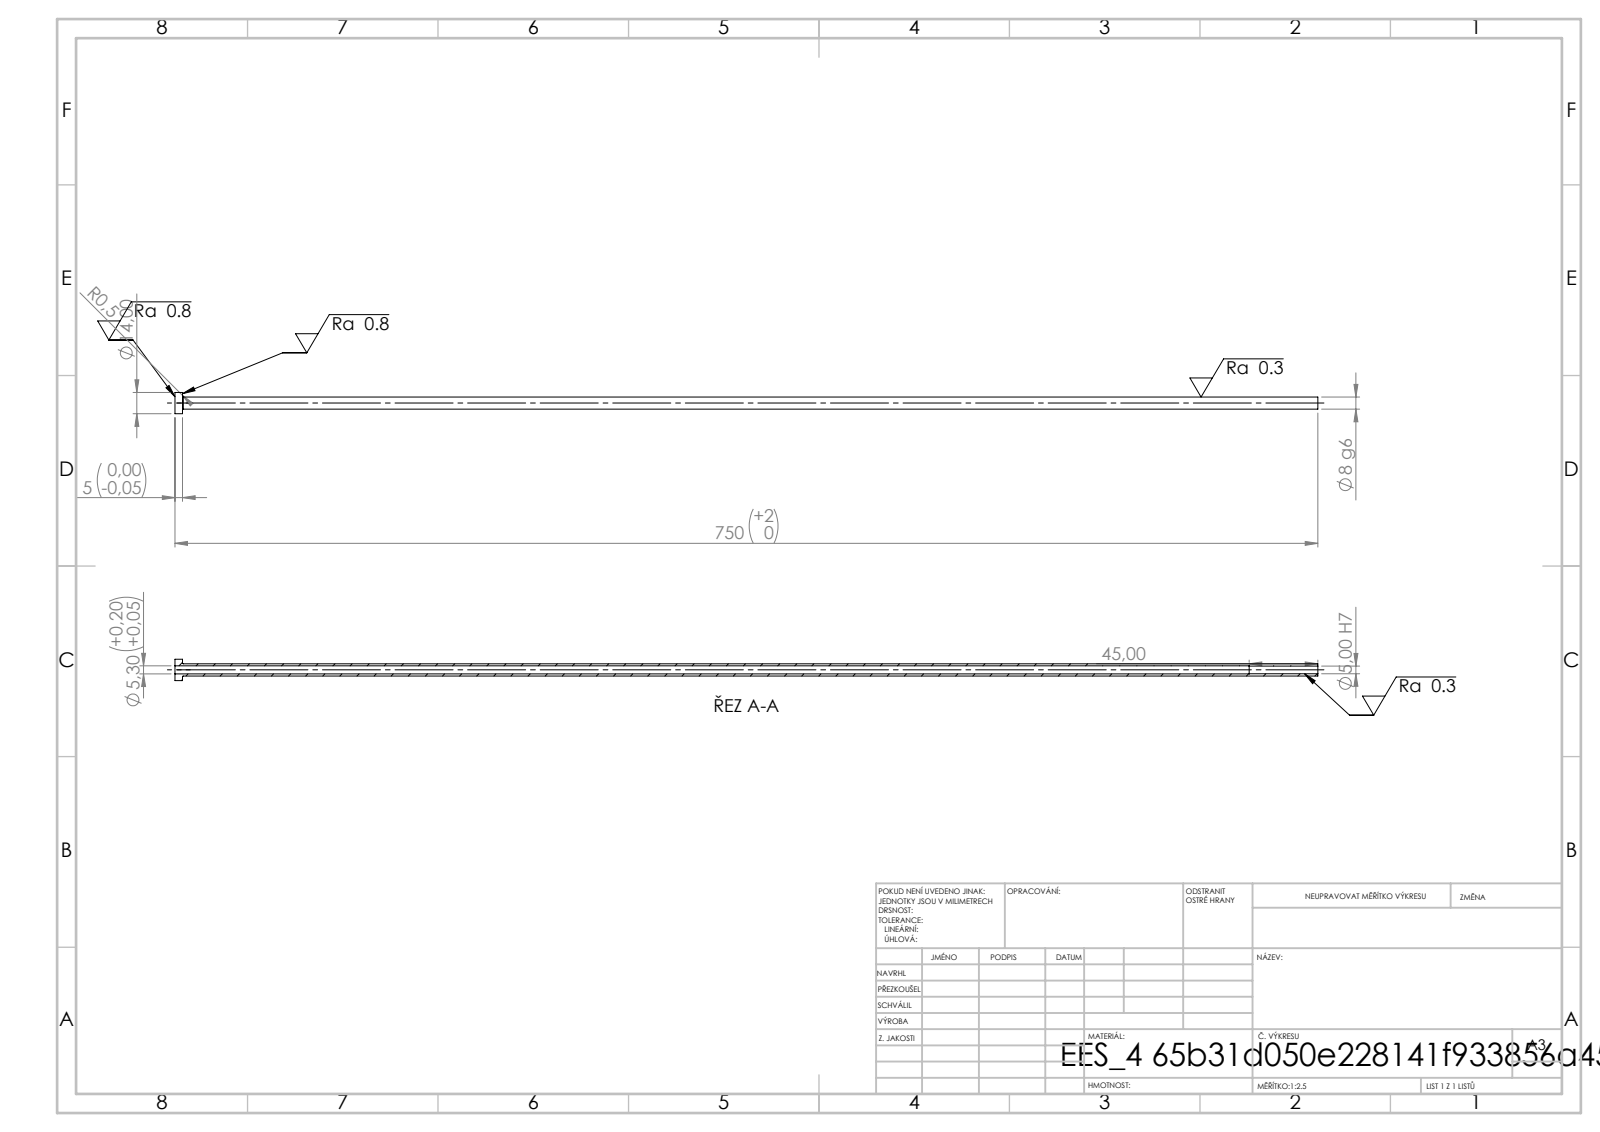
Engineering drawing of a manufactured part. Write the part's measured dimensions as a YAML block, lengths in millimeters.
step_written_by: "SolidWorks 2019 (CONFIG_CONTROL_DESIGN)"
units: millimeters
bodies: {solids: 1, faces: 14, planar: 4, cylindrical: 8, other: 2}
overall_size: [750, 14, 14]
volume: 21782
surface_area: 31653
round_holes:
  - {diameter: 5, count: 1}
  - {diameter: 5.3, count: 1}
round_bosses_or_shafts:
  - {diameter: 14, count: 1}
  - {diameter: 8, count: 1}
face_to_face_distances: [5, 750, 745, 705, 700, 45]
